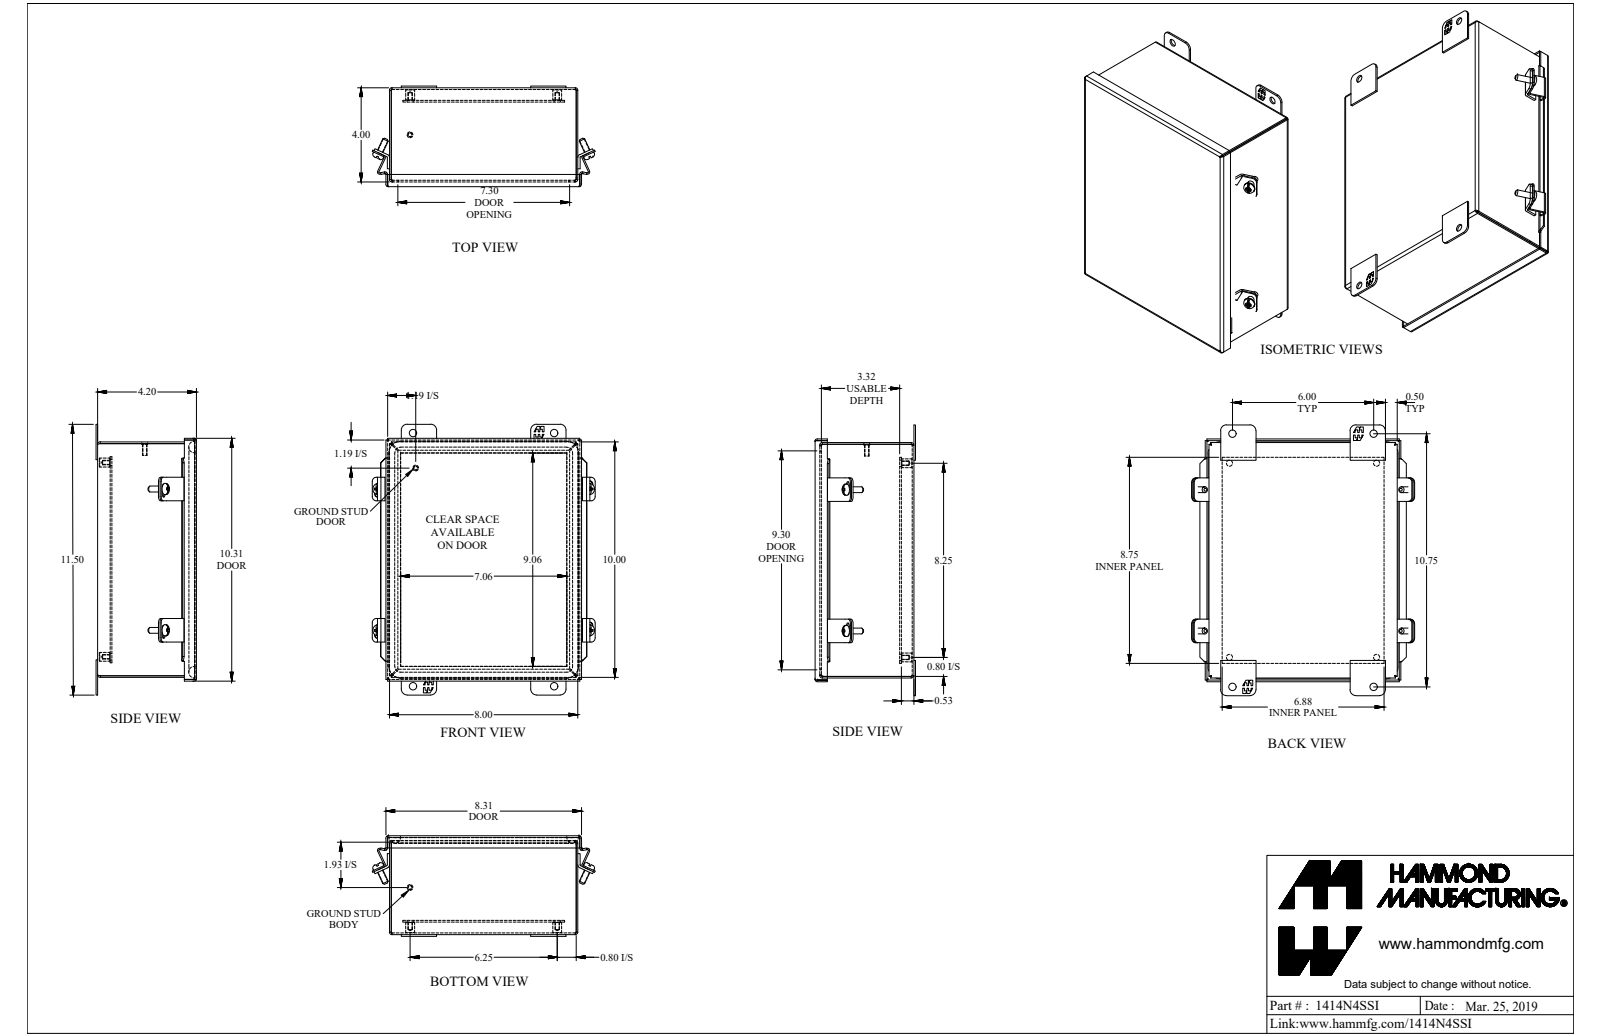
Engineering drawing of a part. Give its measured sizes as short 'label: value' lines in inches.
name: 1414N4SSI
written by: SolidWorks 2018 (AUTOMOTIVE_DESIGN)
unit: in
bodies: 26 solids, 717 faces (473 planar, 168 cylindrical, 76 other)
size: 11.5 × 9.475 × 4.269
volume: 33.35 in³; area: 924.2 in²
holes: 4× ⌀0.156, 4× ⌀0.213, 4× ⌀0.265, 4× ⌀0.313
bosses: 6× ⌀0.25, 4× ⌀0.48, 4× ⌀0.375, 2× ⌀0.19
rounds: 24× R0.25, 16× R0.188, 10× R0.036, 10× R0.108, 8× R0.141, 4× R0.007, 4× R0.01, 4× R0.029
face distances: 0.072, 4.125, 3.593, 0.532, 4.197, 4.053, 7.928, 0.604, 3.665, 0.46
hole spacings: 1.257, 6.252, 9.501, 10.35, 11.304, 6, 6.25, 6.25
